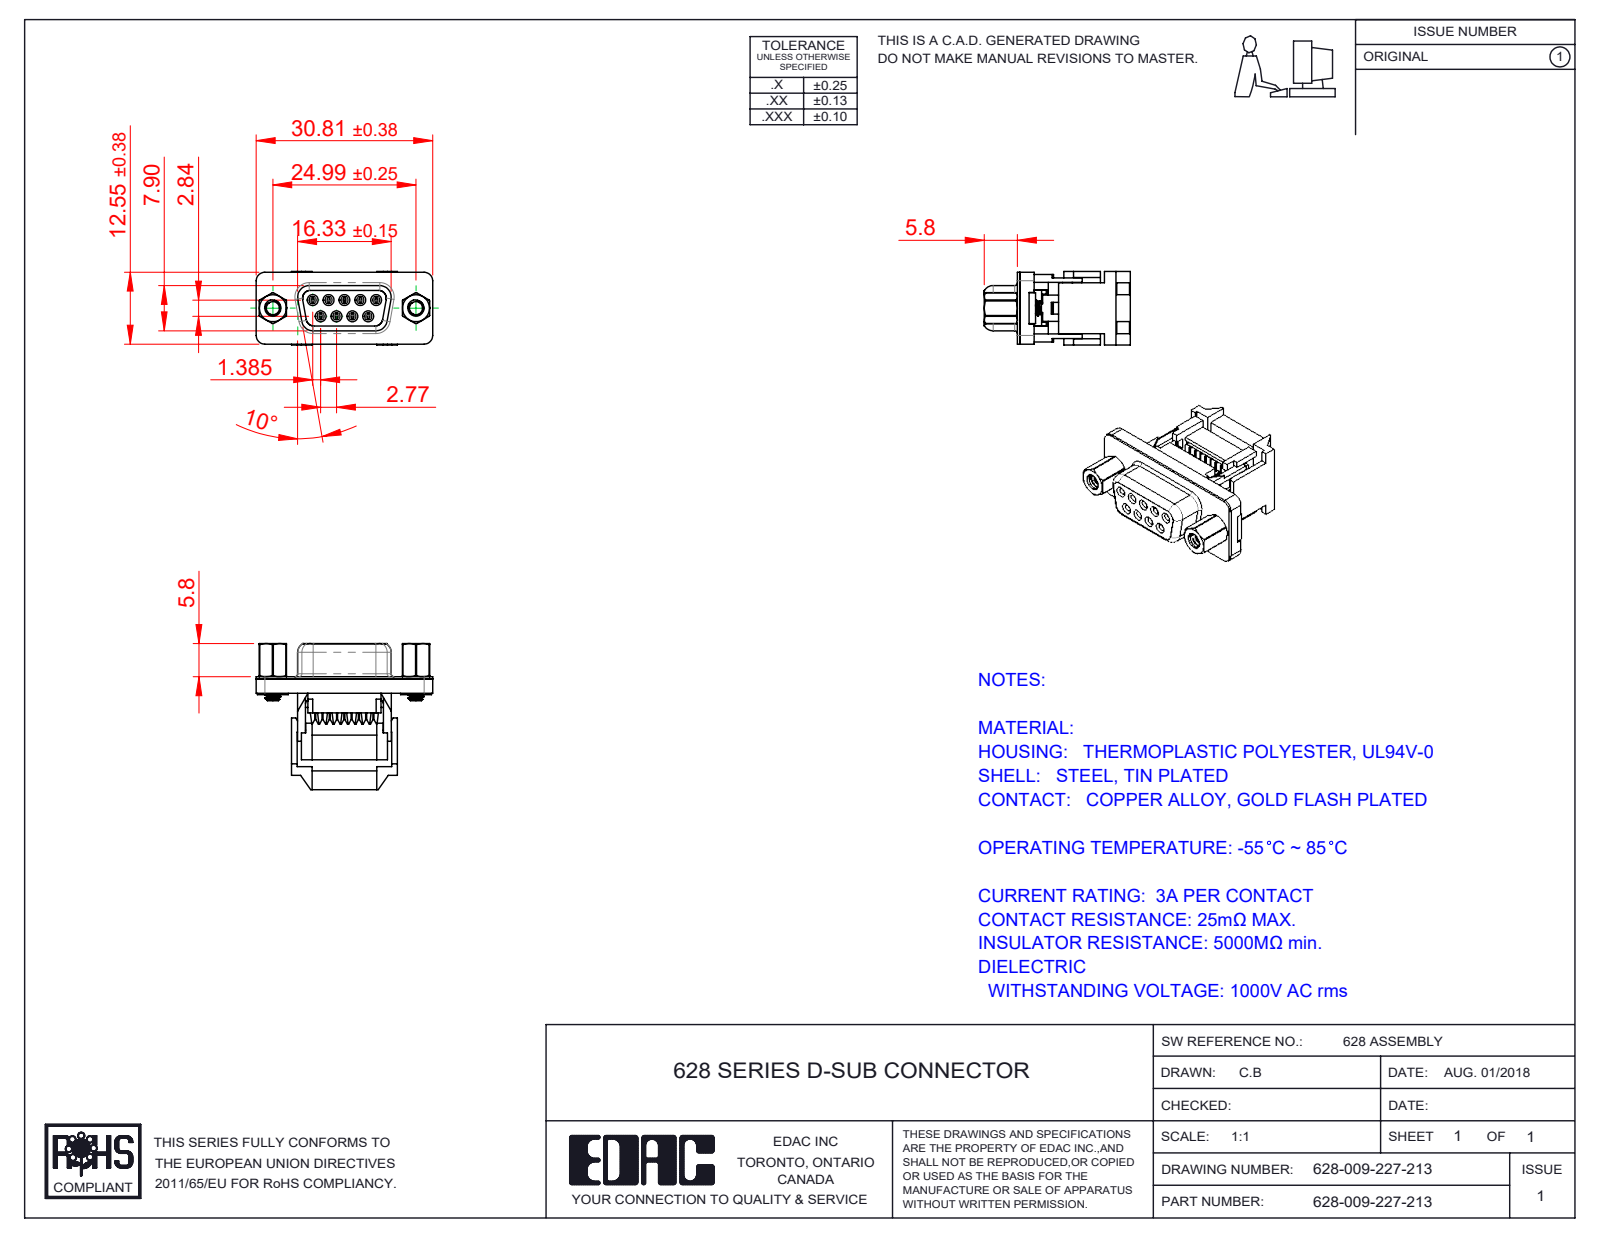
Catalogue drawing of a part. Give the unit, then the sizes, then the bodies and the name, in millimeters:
Units: millimetres
Overall size (bounding box): 30.81 × 25.5 × 12.85
Round holes (diameter × count): ⌀1.2 ×9, ⌀2.26 ×2, ⌀2.29 ×2, ⌀4 ×2, ⌀4.8 ×2, ⌀5 ×2
Round bosses / shafts (diameter × count): ⌀4.9 ×2, ⌀2.79 ×2
Partial cylindrical surfaces — rounded edges, fillets, slot ends (radius × count): R0.9 ×40, R1.2 ×36, R0.5 ×22, R0.15 ×18, R0.64 ×9, R0.65 ×9, R0.89 ×9, R0.94 ×9
Main face-to-face distances: 1.9, 0.4, 1, 2.9, 2.5, 7.05, 1.06, 5.2, 1.03, 7.07
Hole centre spacings: 3.16, 2.77, 5.54, 5.03, 5.04, 8.31, 7.48, 7.49
Volume: 3 361 mm³ · Surface area: 7 125 mm²
Bodies: 20 solids, 1909 faces (1134 planar, 435 cylindrical, 340 other)
Part name (STEP PRODUCT): 628 PB Shell_09 Contacts; 628-009-227-213; 628 IDC 4-40 Threaded Rivet; 628 IDC Cable Cover_09 Contacts (+5 more)
STEP written by: SolidWorks 2020 (CONFIG_CONTROL_DESIGN)
